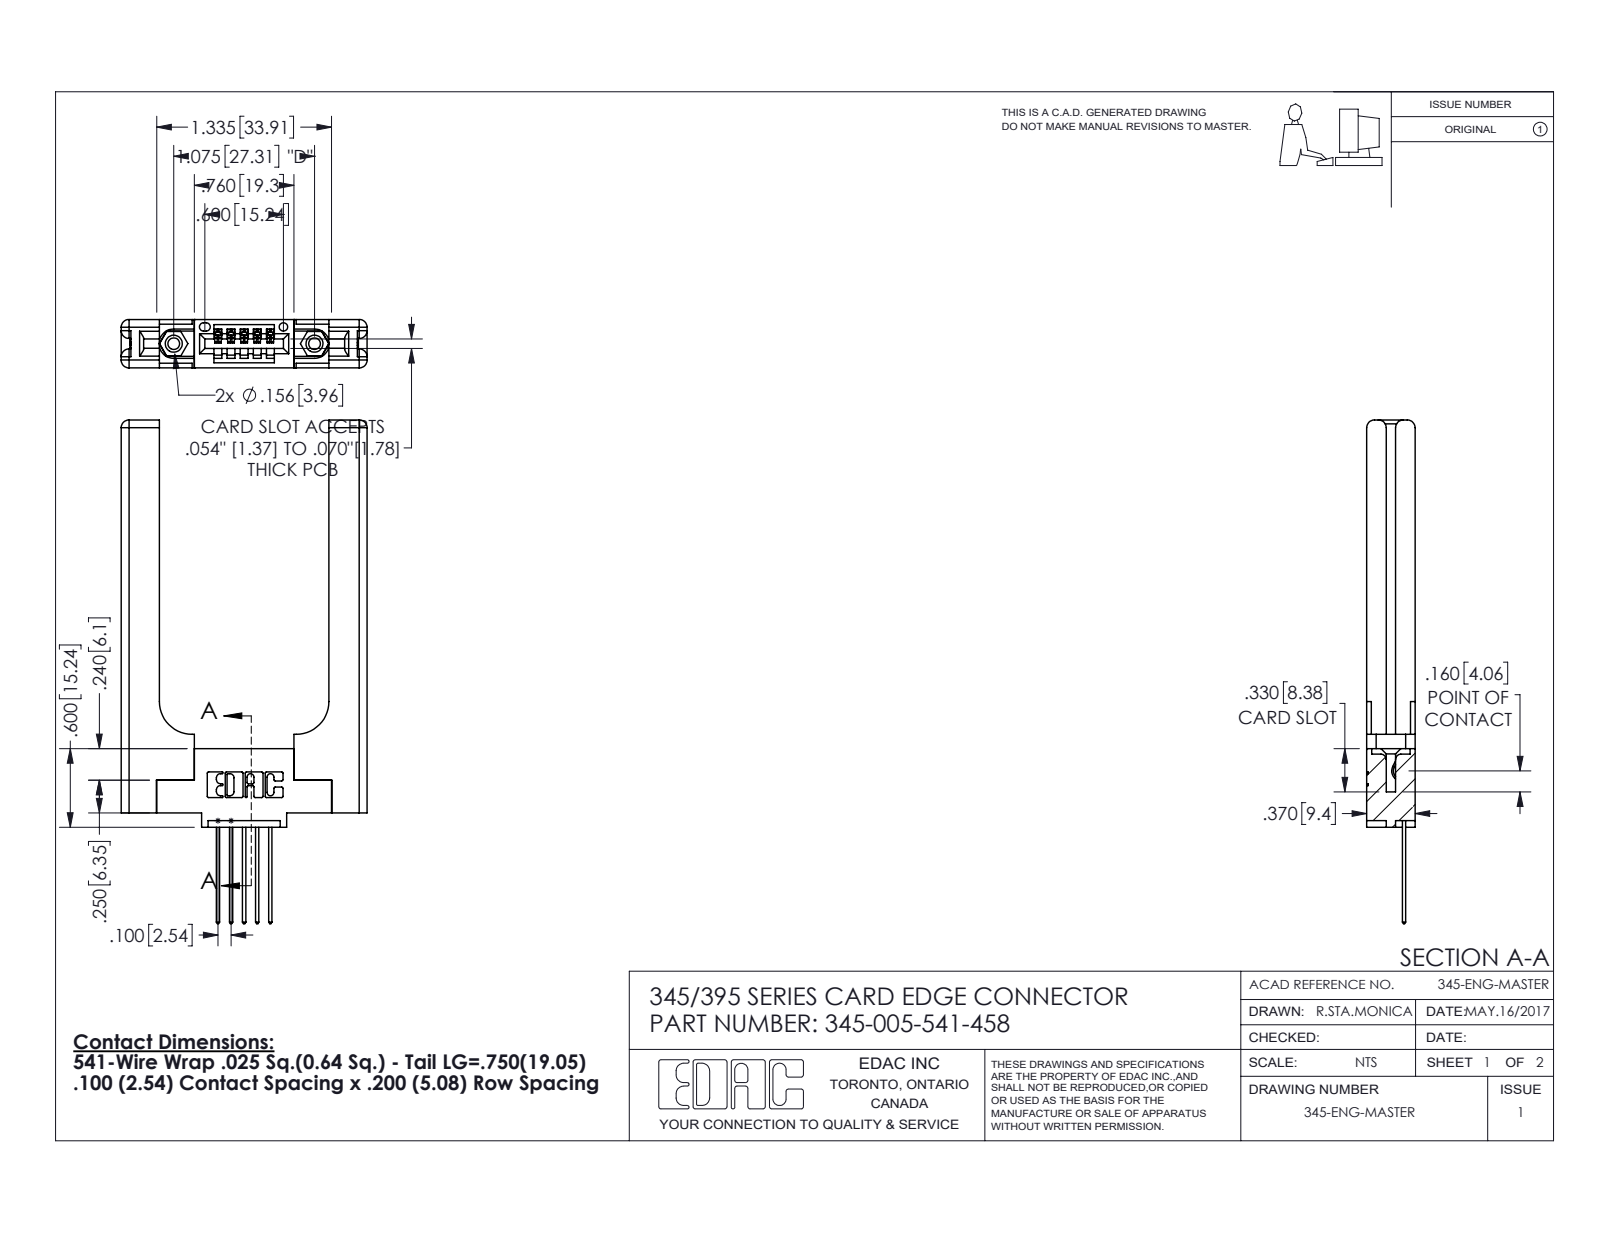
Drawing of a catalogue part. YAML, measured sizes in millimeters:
part_name: "345 Part_0.110 Offset - 0.156 Dia-TH; 345-220-058_345-220-058; 345-005-541-458; 345-292-001_345-293-141 (+1 more)"
step_written_by: "SolidWorks 2016 (CONFIG_CONTROL_DESIGN)"
units: millimeters
bodies: {solids: 10, faces: 676, planar: 432, cylindrical: 184, other: 60}
overall_size: [97.7, 47.7, 9.4]
volume: 12700
surface_area: 10530
round_holes:
  - {diameter: 2.3, count: 2}
  - {diameter: 3.2, count: 2}
  - {diameter: 4, count: 2}
  - {diameter: 1.6, count: 1}
round_bosses_or_shafts:
  - {diameter: 3.9, count: 2}
partial_cylinders:
  - {radius: 0.3, count: 22}
  - {radius: 1.5, count: 16}
  - {radius: 0.2, count: 10}
  - {radius: 0.3, count: 10}
  - {radius: 0.2, count: 6}
  - {radius: 0.8, count: 6}
  - {radius: 0.7, count: 3}
  - {radius: 0.8, count: 2}
face_to_face_distances: [9.4, 3.8, 5.6, 1.8, 32.9, 3.8, 2, 7.6, 1.8, 7.4]
hole_center_spacings: [6.9, 21.5, 27.3]
